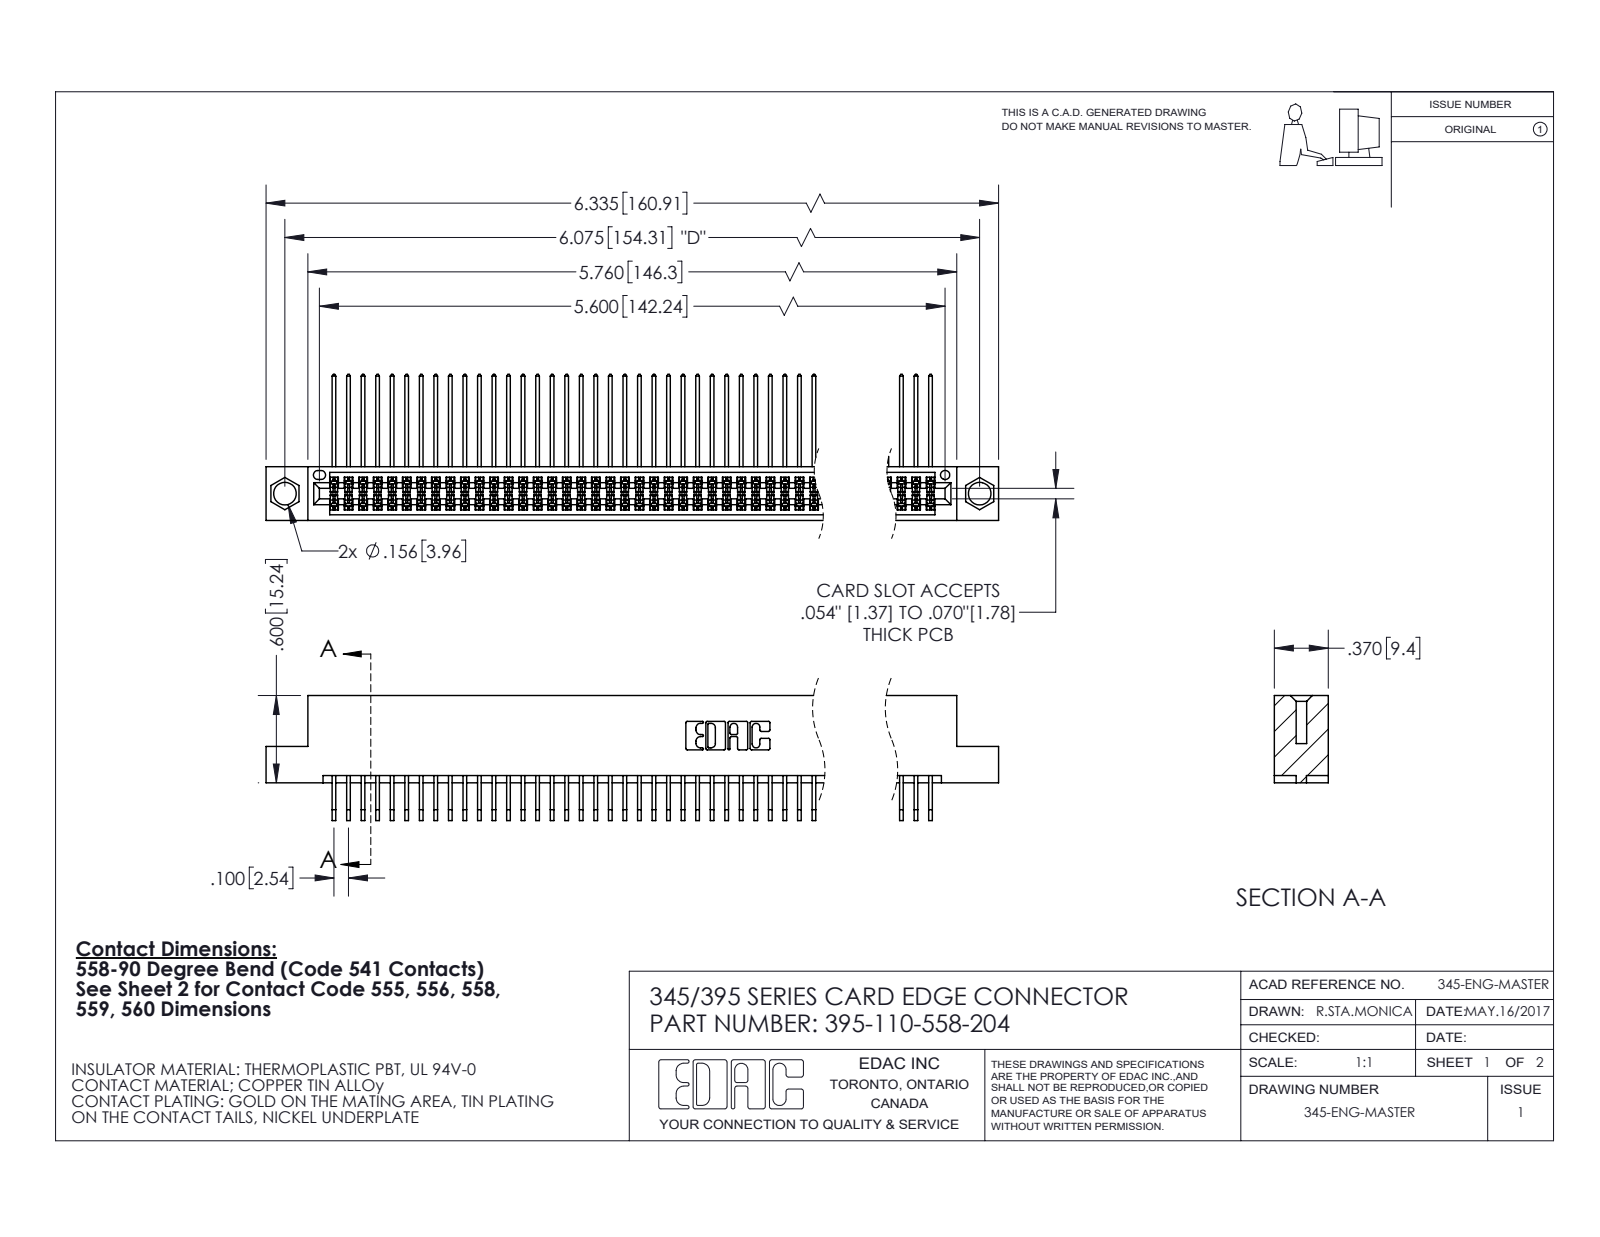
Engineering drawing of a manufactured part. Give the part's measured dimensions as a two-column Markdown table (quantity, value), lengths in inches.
| quantity | value |
| --- | --- |
| part name | 345-292-001_558 Tail - 2; 345 Part_Flush Mounting Lugs - 0.156 Dia-TI; 395-110-558-204; 345-292-001_558 559 Tail - 1 |
| STEP written by | SolidWorks 2020 (CONFIG_CONTROL_DESIGN) |
| units | inches |
| bodies | 111 solids, 5860 faces (3944 planar, 1916 cylindrical, 0 other) |
| overall size | 6.335 × 1.005 × 0.859 |
| volume | 0.993 in³ |
| surface area | 42.09 in² |
| round holes (diameter × count) | 0.156 × 2, 0.064 × 1 |
| partial cylindrical surfaces (radius × count) | 0.006 × 220, 0.01 × 22, 0.007 × 6, 0.031 × 6, 0.026 × 3, 0.014 × 2, 0.019 × 2, 0.022 × 2 |
| main face-to-face distances | 0.072, 0.298, 0.2, 0.37, 0.098, 0.272, 0.025, 0.225, 0.025, 0.175 |
| hole center spacings | 0.27, 5.839, 6.075 |
